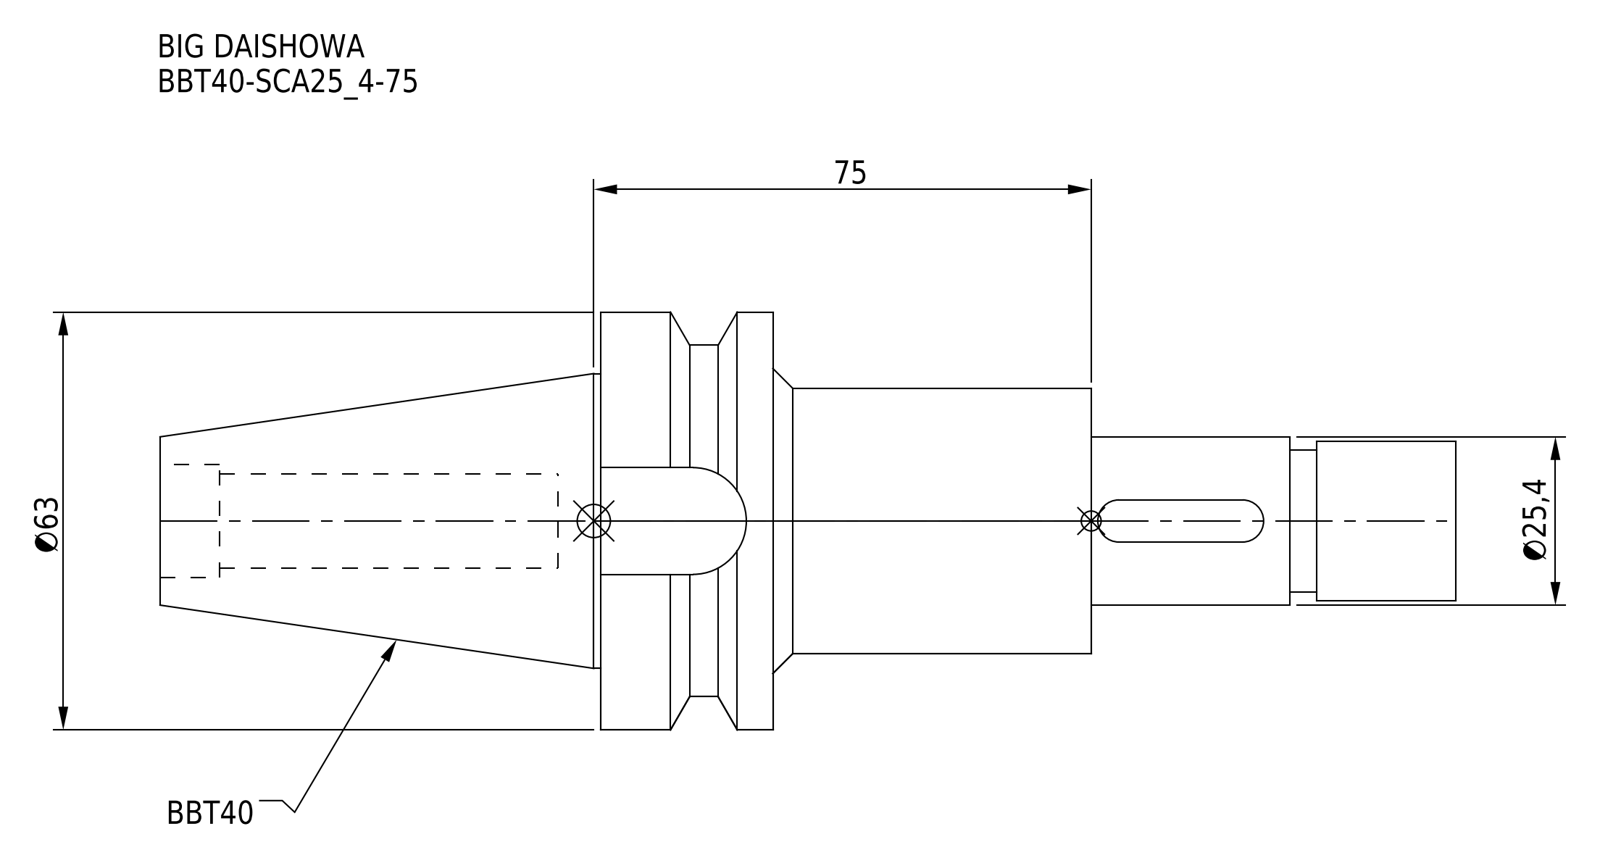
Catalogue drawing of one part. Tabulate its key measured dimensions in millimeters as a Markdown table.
| quantity | value |
| --- | --- |
| part name | BBT40-SCA25_4-75 |
| STEP written by | CREO PARAMETRIC BY PTC INC, 2016380 (AUTOMOTIVE_DESIGN) |
| units | millimeters |
| bodies | 1 solid, 50 faces (18 planar, 24 cylindrical, 8 other) |
| overall size | 195.4 × 63 × 63 |
| volume | 212 890 mm³ |
| surface area | 31 966 mm² |
| round holes (diameter × count) | 14.2 × 1, 17 × 1 |
| round bosses / shafts (diameter × count) | 63 × 1, 53 × 1, 44.45 × 1, 40 × 1, 25.4 × 1, 24 × 1, 21.5 × 1 |
| partial cylindrical surfaces (radius × count) | 3.17 × 2, 8.05 × 1 |
| main face-to-face distances | 26, 48, 74, 55, 103, 129, 45, 195.4, 140.4, 92.4 |
